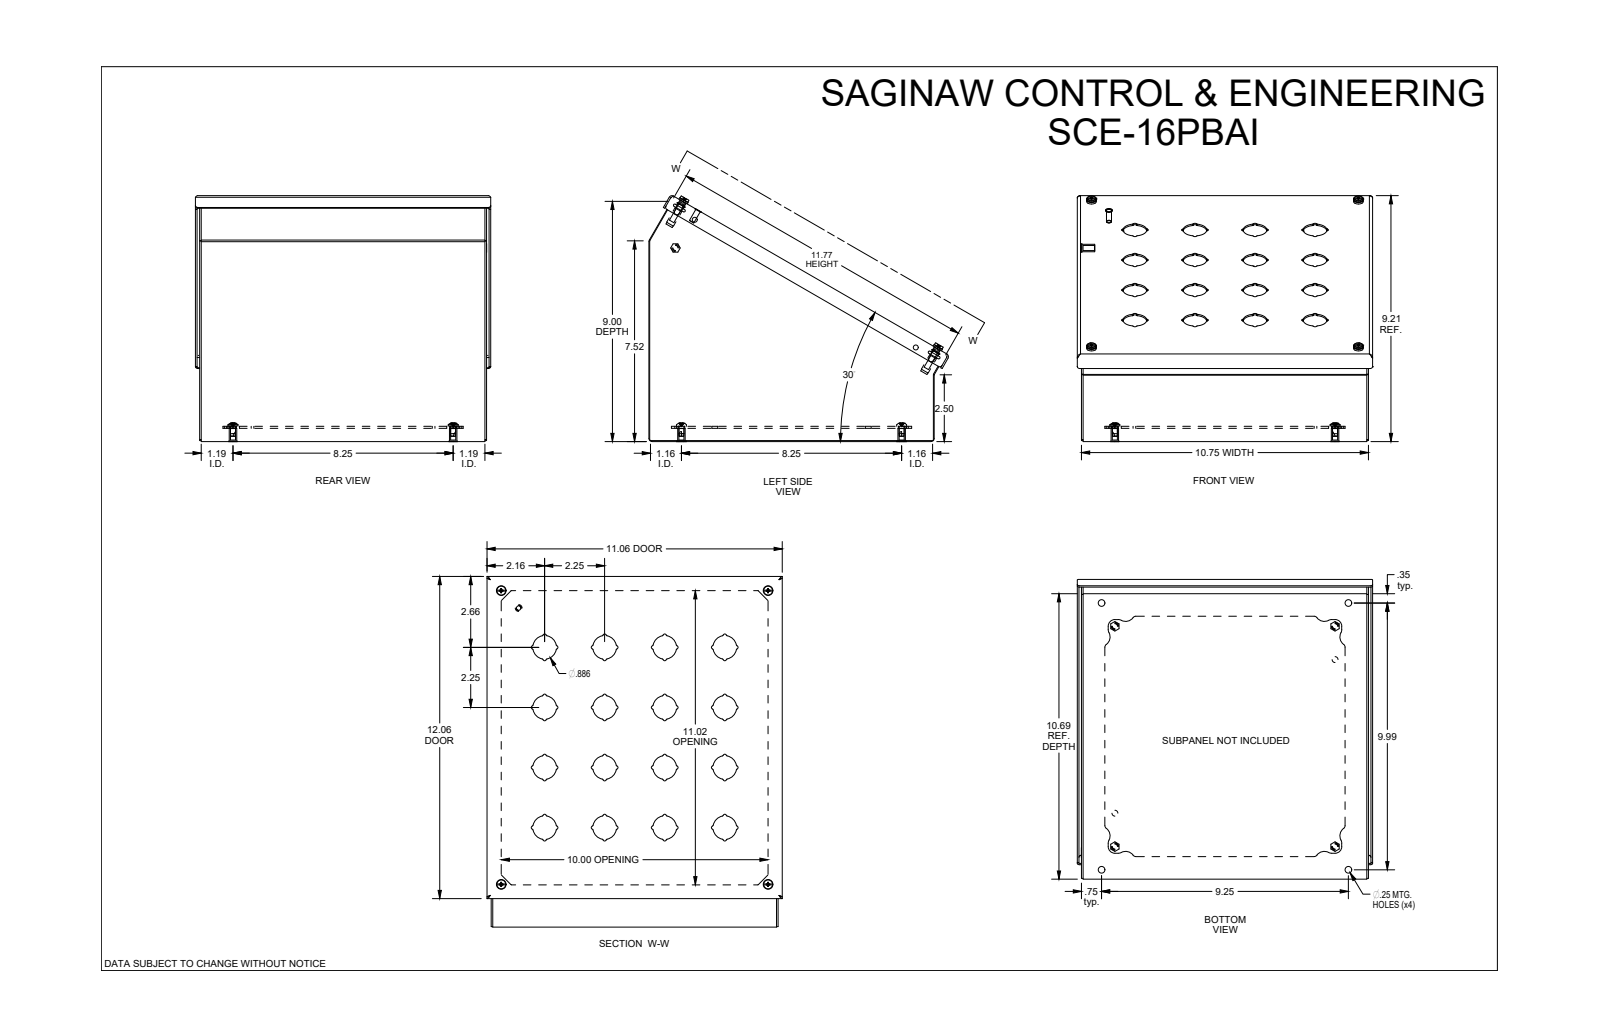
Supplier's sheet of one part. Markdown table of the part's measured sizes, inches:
| quantity | value |
| --- | --- |
| part name | SCE-16PBAI |
| STEP written by | SolidWorks 2021 (AUTOMOTIVE_DESIGN) |
| units | inches |
| bodies | 11 solids, 937 faces (259 planar, 429 cylindrical, 249 other) |
| overall size | 11.246 × 11.063 × 9.233 |
| volume | 39.69 in³ |
| surface area | 1 291 in² |
| round holes (diameter × count) | 0.25 × 16, 0.19 × 9, 0.266 × 4, 0.317 × 4, 0.218 × 2, 0.193 × 1 |
| round bosses / shafts (diameter × count) | 0.188 × 8, 0.28 × 5, 0.373 × 4, 0.34 × 4, 0.334 × 4, 0.292 × 4, 0.27 × 4, 0.146 × 4 |
| partial cylindrical surfaces (radius × count) | 0.04 × 128, 0.062 × 64, 0.443 × 16, 0.25 × 12, 0.01 × 8, 0.03 × 8, 0.06 × 8, 0.115 × 8 |
| main face-to-face distances | 0.06, 10.69, 10.63, 0.496, 0.436, 0.571, 0.511, 0.075, 10.75, 0.156 |
| hole center spacings | 10, 11.016, 1.004, 8.25, 8.793, 9.134, 9.442, 10 |
